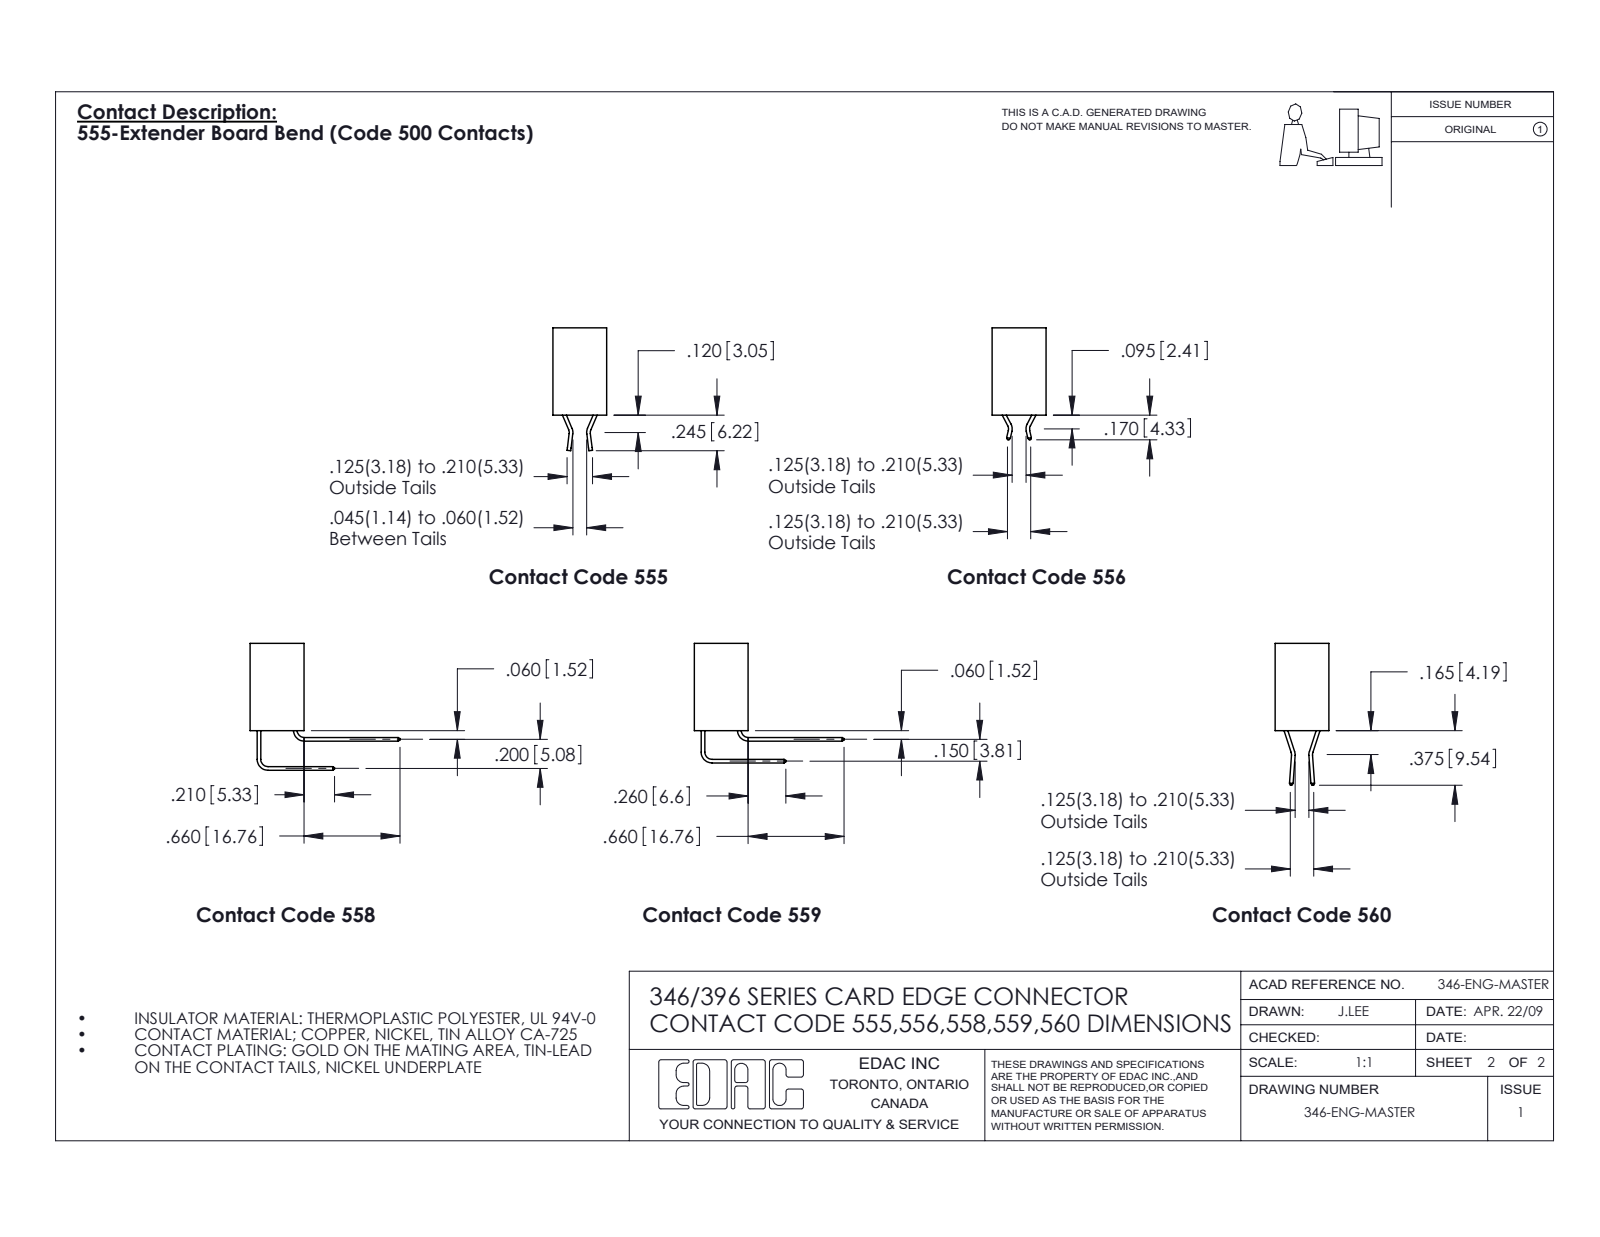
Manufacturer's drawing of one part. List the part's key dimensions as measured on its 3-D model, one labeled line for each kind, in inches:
Part name (STEP PRODUCT): 346 Part_Flush Mounting Lugs - 0.156 Dia-TH; 396-026-540-103; 345-292-001_345-293-140; 345-250-002_345-250-002-102
STEP written by: SolidWorks 2016 (CONFIG_CONTROL_DESIGN)
Units: inches
Bodies: 29 solids, 1668 faces (1126 planar, 534 cylindrical, 8 other)
Overall size (bounding box): 4.06 × 1.16 × 0.37
Volume: 0.599 in³ · Surface area: 19.49 in²
Round holes (diameter × count): ⌀0.116 ×2, ⌀0.156 ×2, ⌀0.064 ×1
Round bosses / shafts (diameter × count): ⌀0.25 ×2, ⌀0.18 ×2, ⌀0.136 ×2
Partial cylindrical surfaces — rounded edges, fillets, slot ends (radius × count): R0.006 ×52, R0.01 ×52, R0.01 ×22, R0.007 ×6, R0.031 ×6, R0.026 ×3, R0.031 ×2, R0.04 ×2
Main face-to-face distances: 0.048, 0.322, 0.25, 0.37, 0.025, 0.072, 0.298, 0.148, 0.222, 0.1
Hole centre spacings: 0.246, 3.587, 3.795
